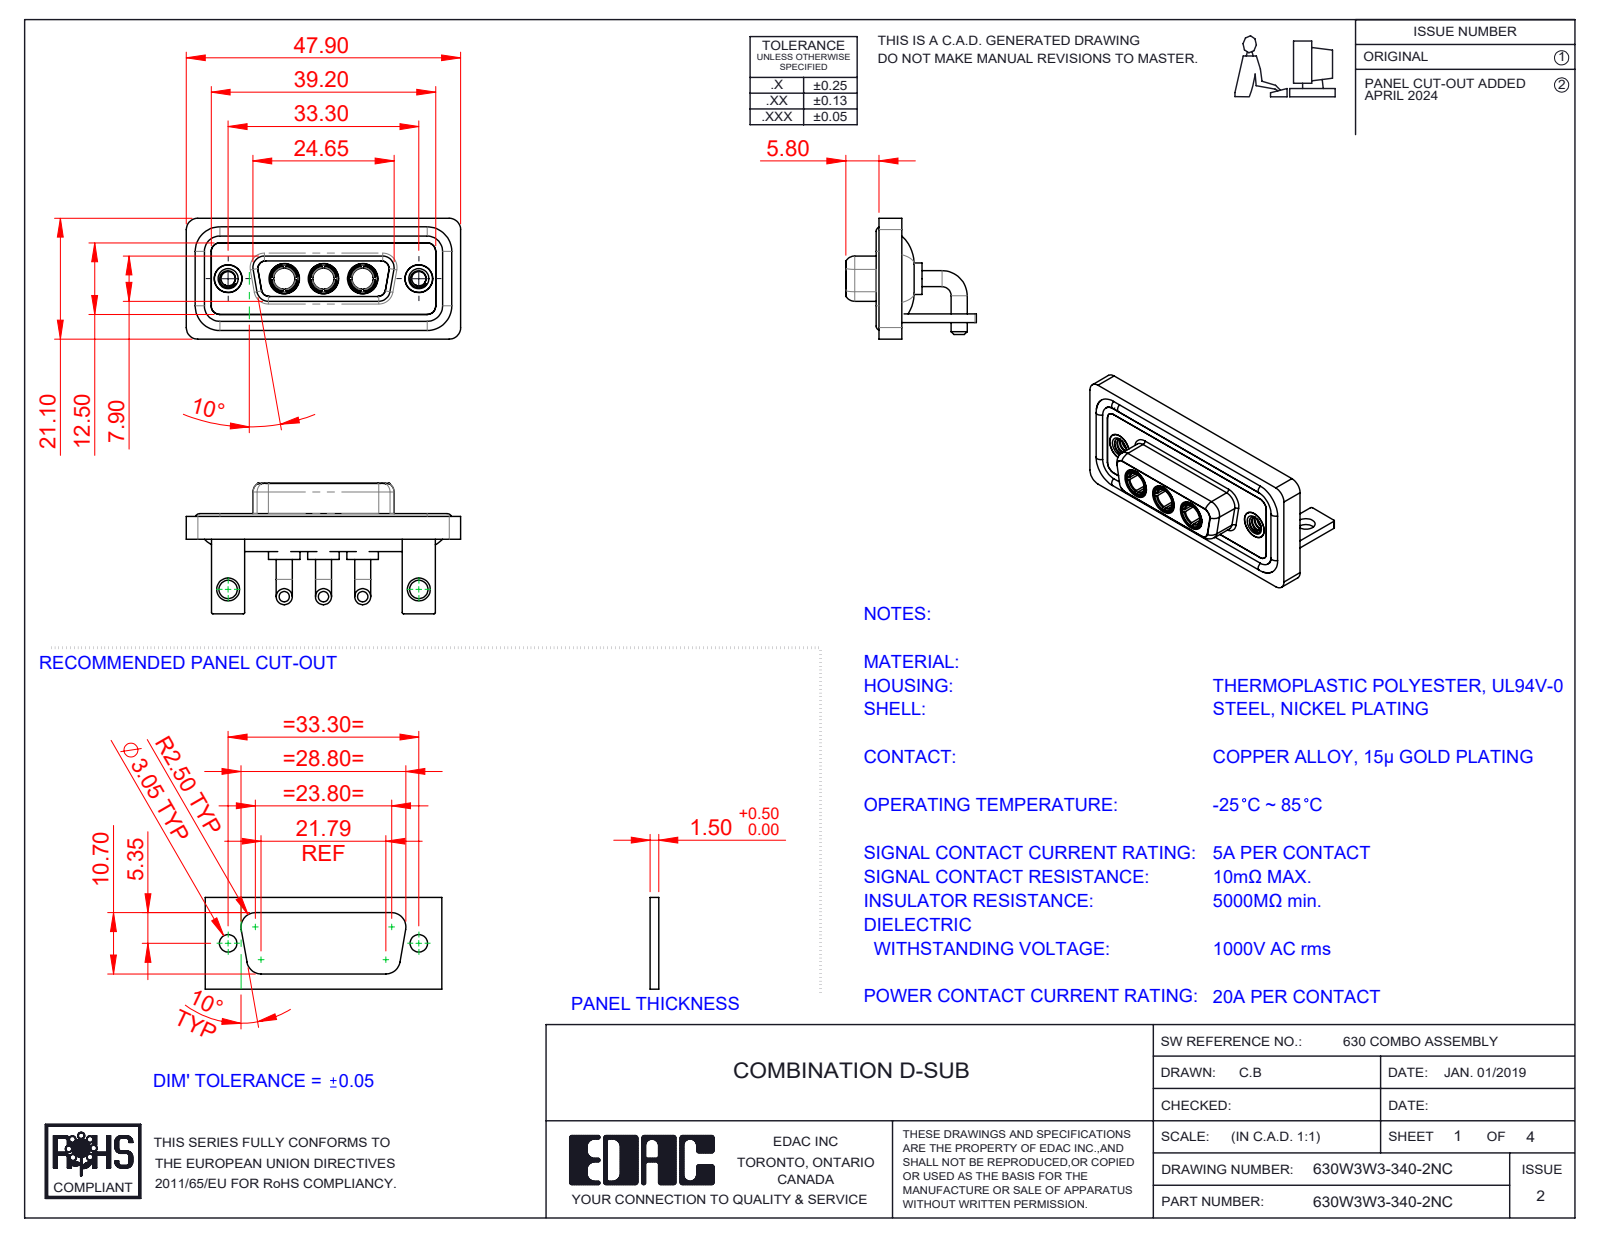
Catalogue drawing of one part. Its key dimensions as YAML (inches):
part_name: "630Combo Waterproof Housing_15 Contacts; 630W3W3-340-2NC; 630Combo Housing_3W3; 630Combo Stabilizer Bracket_50 Contacts (+4 more)"
step_written_by: "SolidWorks 2023 (CONFIG_CONTROL_DESIGN)"
units: inches
bodies: {solids: 15, faces: 662, planar: 212, cylindrical: 285, other: 165}
overall_size: [1.886, 0.898, 0.831]
volume: 0.399
surface_area: 16.6
round_holes:
  - {diameter: 0.191, count: 5}
  - {diameter: 0.146, count: 3}
  - {diameter: 0.209, count: 3}
  - {diameter: 0.098, count: 2}
  - {diameter: 0.126, count: 2}
  - {diameter: 0.157, count: 2}
  - {diameter: 0.159, count: 2}
  - {diameter: 0.197, count: 2}
round_bosses_or_shafts:
  - {diameter: 0.11, count: 6}
  - {diameter: 0.063, count: 4}
  - {diameter: 0.217, count: 3}
  - {diameter: 0.205, count: 3}
  - {diameter: 0.195, count: 3}
  - {diameter: 0.187, count: 3}
  - {diameter: 0.148, count: 3}
  - {diameter: 0.195, count: 2}
partial_cylinders:
  - {radius: 0.079, count: 21}
  - {radius: 0.059, count: 18}
  - {radius: 0.01, count: 16}
  - {radius: 0.053, count: 12}
  - {radius: 0.063, count: 8}
  - {radius: 0.02, count: 5}
  - {radius: 0.024, count: 4}
  - {radius: 0.026, count: 4}
face_to_face_distances: [0.016, 0.114, 0.059, 0.071, 0.146, 0.043, 0.161, 0.063, 0.098, 0.055]
hole_center_spacings: [0.27, 0.386, 0.656, 0.925, 1.311, 0.539]
